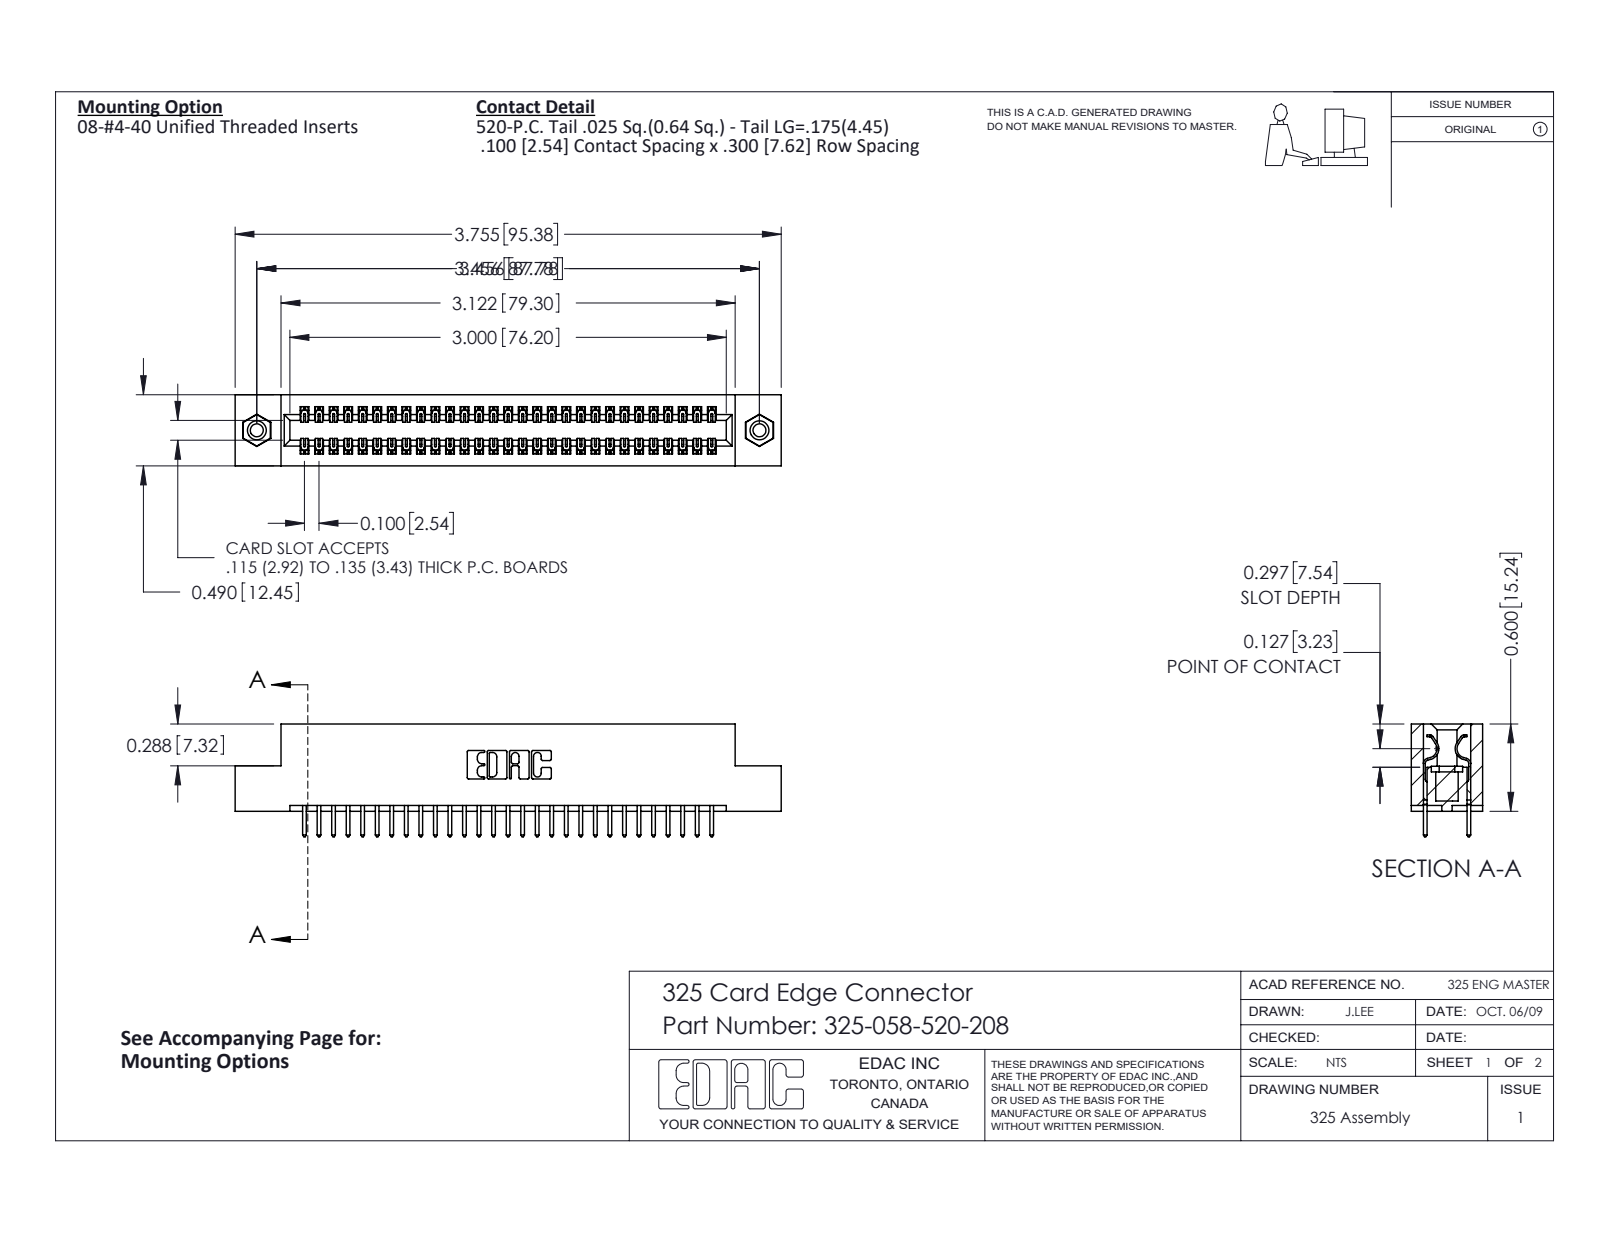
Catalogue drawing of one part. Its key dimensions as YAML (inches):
part_name: "325-292-001_325-293-120; 325 Part_TI; 325-058-520-208; 345-250-001_345-250-003-102"
step_written_by: "SolidWorks 2016 (CONFIG_CONTROL_DESIGN)"
units: inches
bodies: {solids: 61, faces: 3190, planar: 2190, cylindrical: 984, other: 16}
overall_size: [3.755, 0.775, 0.49]
volume: 0.743
surface_area: 22.21
round_holes:
  - {diameter: 0.089, count: 2}
  - {diameter: 0.125, count: 2}
  - {diameter: 0.16, count: 2}
round_bosses_or_shafts:
  - {diameter: 0.155, count: 2}
partial_cylinders:
  - {radius: 0.006, count: 87}
  - {radius: 0.01, count: 58}
  - {radius: 0.01, count: 22}
  - {radius: 0.007, count: 6}
  - {radius: 0.031, count: 6}
  - {radius: 0.026, count: 3}
  - {radius: 0.014, count: 2}
  - {radius: 0.022, count: 2}
face_to_face_distances: [0.083, 0.407, 0.3, 0.49, 0.107, 0.383, 0.025, 0.325, 0.04, 0.275]
hole_center_spacings: [3.456]
